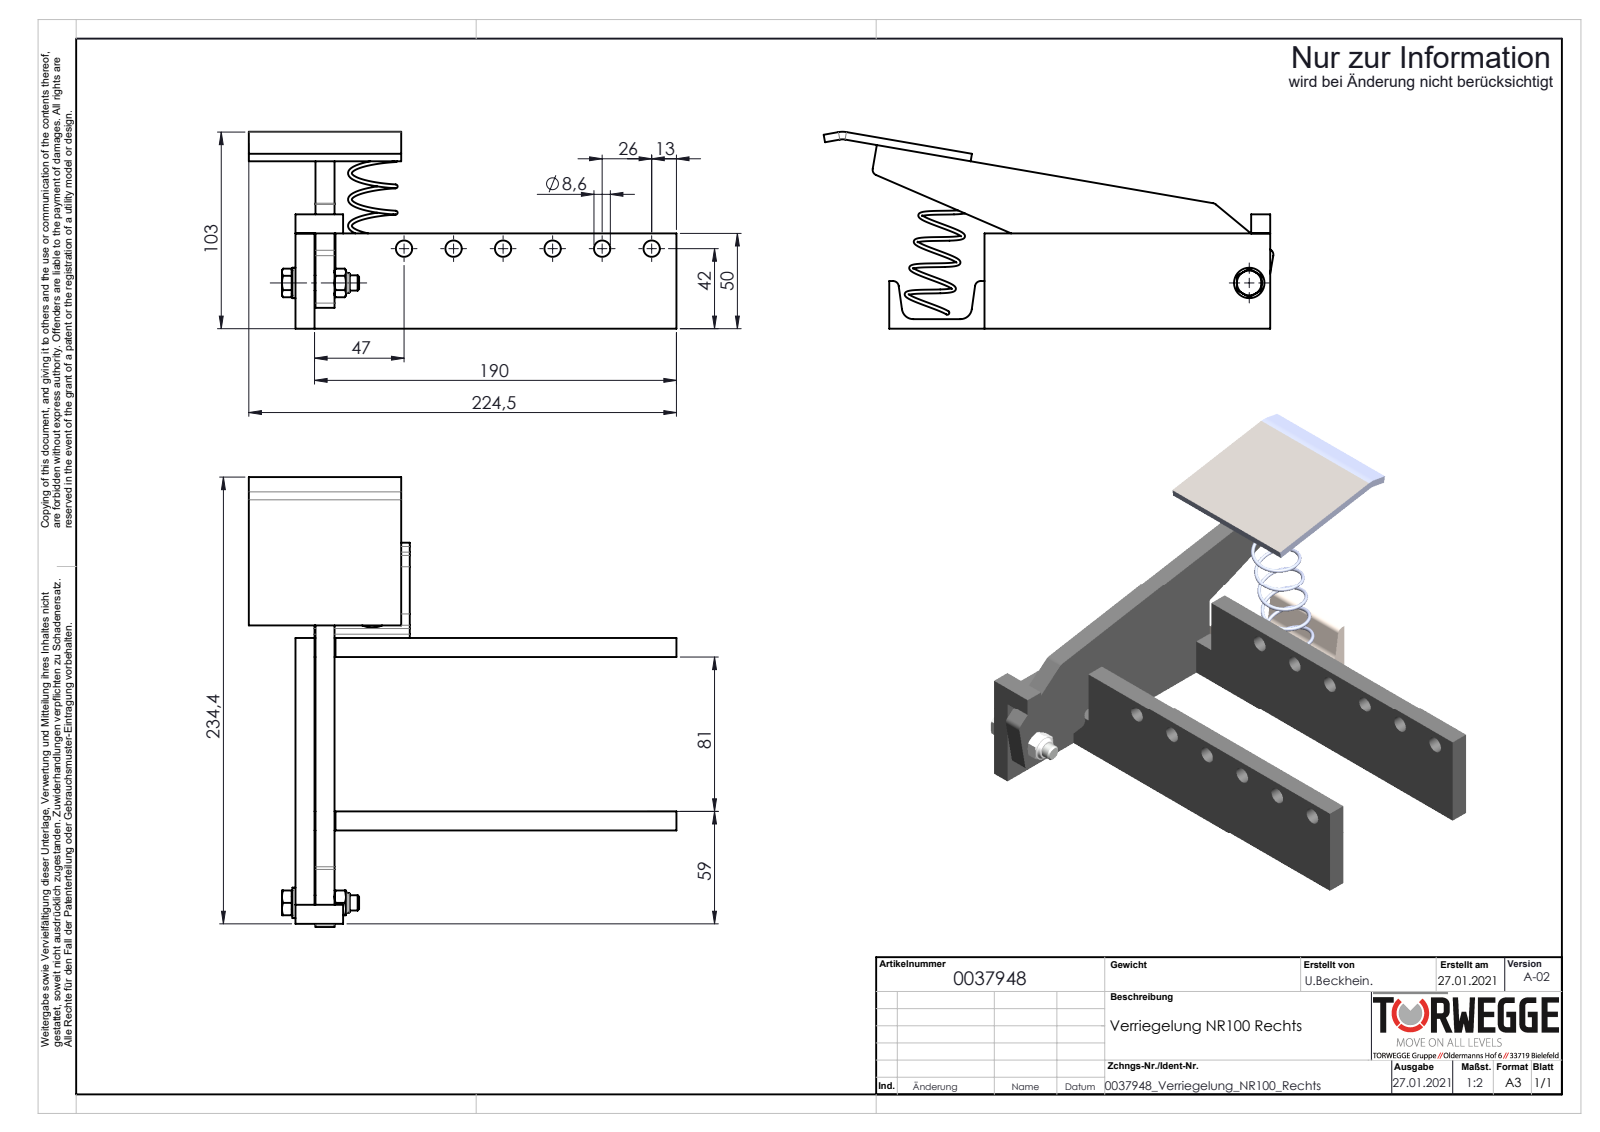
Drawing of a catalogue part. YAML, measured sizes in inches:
part_name: "0037948"
step_written_by: "SolidWorks 2020 (AUTOMOTIVE_DESIGN)"
units: inches
bodies: {solids: 11, faces: 176, planar: 89, cylindrical: 51, other: 36}
overall_size: [9.295, 8.839, 4.069]
volume: 23.35
surface_area: 182.1
round_holes:
  - {diameter: 0.339, count: 6}
  - {diameter: 0.268, count: 1}
  - {diameter: 0.331, count: 1}
  - {diameter: 0.335, count: 1}
round_bosses_or_shafts:
  - {diameter: 0.63, count: 1}
  - {diameter: 0.512, count: 1}
  - {diameter: 0.315, count: 1}
partial_cylinders:
  - {radius: 0.118, count: 9}
  - {radius: 0.236, count: 2}
  - {radius: 0.315, count: 1}
  - {radius: 0.472, count: 1}
face_to_face_distances: [0.394, 3.583, 0.413, 3.976, 3.189, 0.02, 0.807, 1.969, 0.157, 2.362]
hole_center_spacings: [1.024, 2.047, 3.071, 4.094, 5.118]
